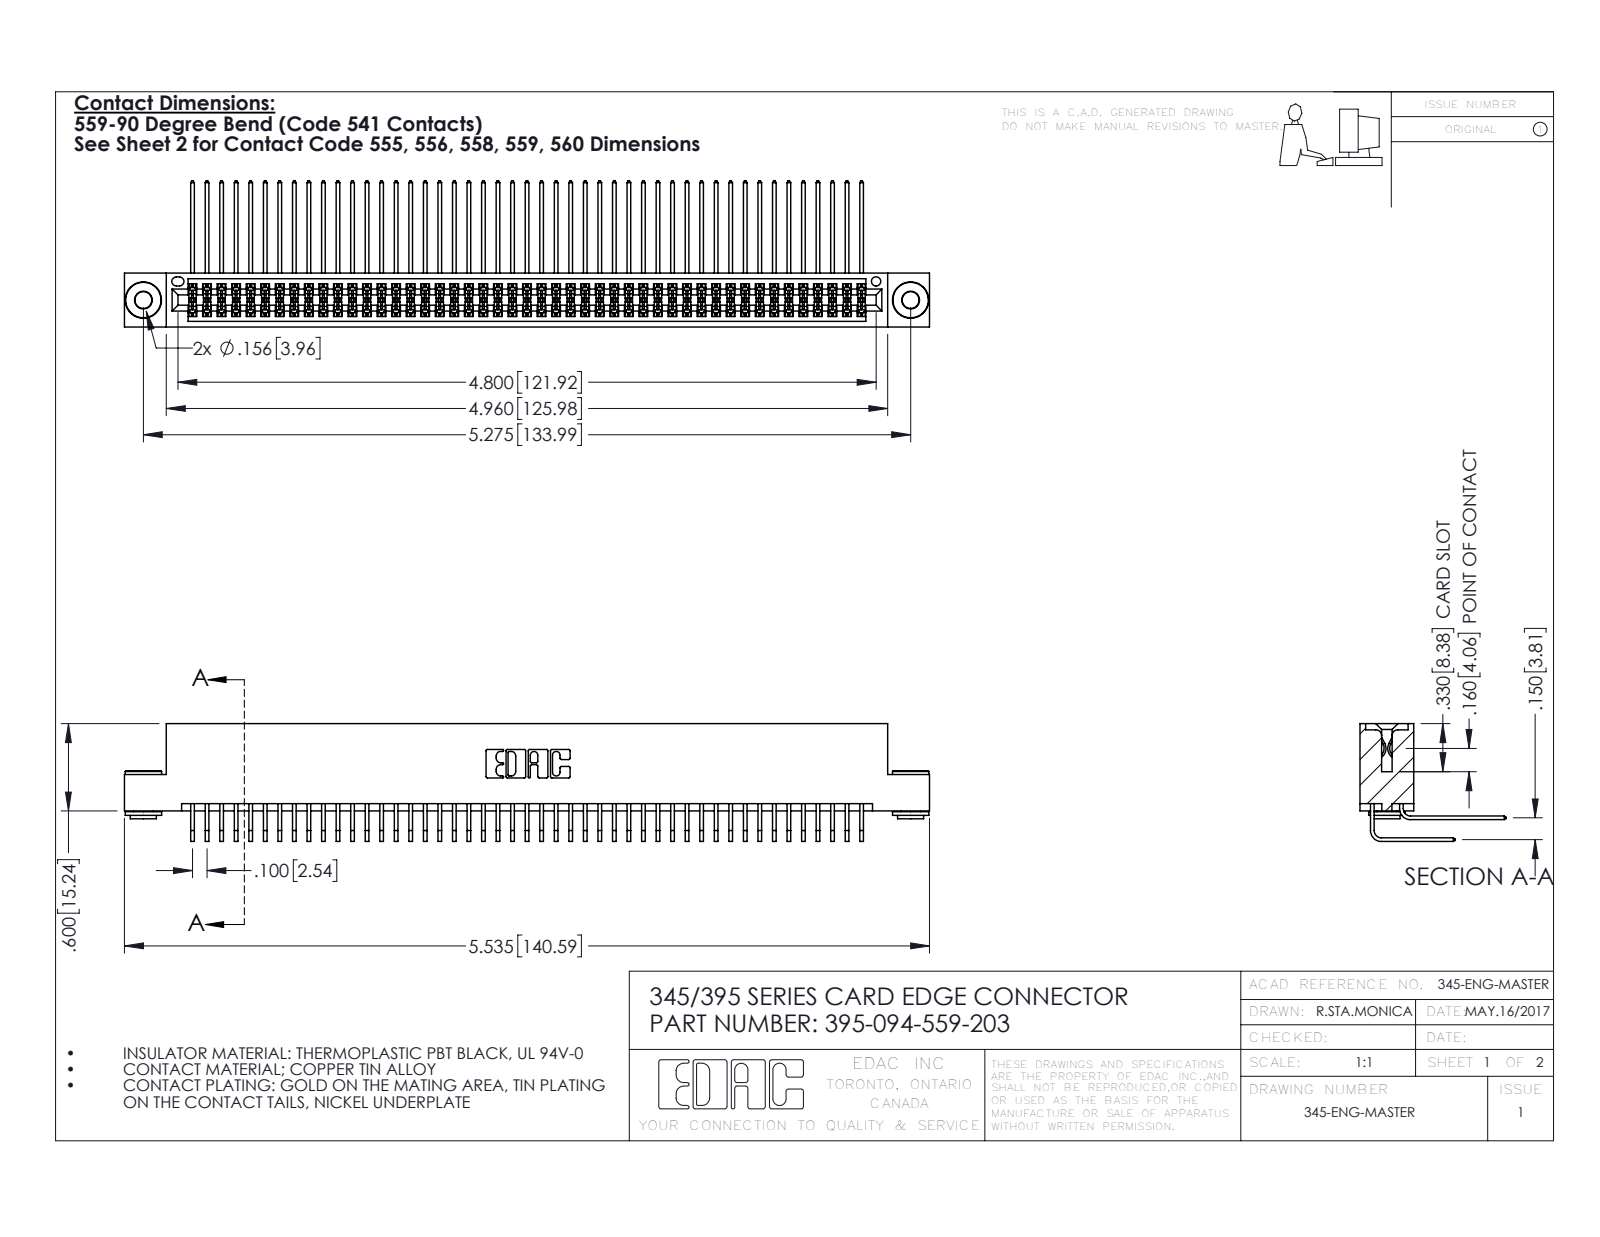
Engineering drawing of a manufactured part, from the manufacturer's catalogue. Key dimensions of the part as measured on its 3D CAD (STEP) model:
Part name (STEP PRODUCT): 345-250-002_345-250-002-102; 395-094-559-203; 345-292-001_559 Tail - 2; 345 Part_Flush Mounting Lugs - 0.156 Dia-TH (+1 more)
STEP written by: SolidWorks 2016 (CONFIG_CONTROL_DESIGN)
Units: inches
Bodies: 97 solids, 5052 faces (3380 planar, 1664 cylindrical, 8 other)
Overall size (bounding box): 5.535 × 1.005 × 0.809
Volume: 0.871 in³ · Surface area: 37.1 in²
Round holes (diameter × count): ⌀0.116 ×2, ⌀0.156 ×2, ⌀0.064 ×1
Round bosses / shafts (diameter × count): ⌀0.25 ×2, ⌀0.18 ×2, ⌀0.136 ×2
Partial cylindrical surfaces — rounded edges, fillets, slot ends (radius × count): R0.006 ×141, R0.01 ×22, R0.007 ×6, R0.031 ×6, R0.026 ×3, R0.014 ×2, R0.019 ×2, R0.022 ×2
Main face-to-face distances: 0.072, 0.298, 0.2, 0.37, 0.025, 0.098, 0.272, 0.225, 0.175, 0.15
Hole centre spacings: 0.27, 5.039, 5.275
